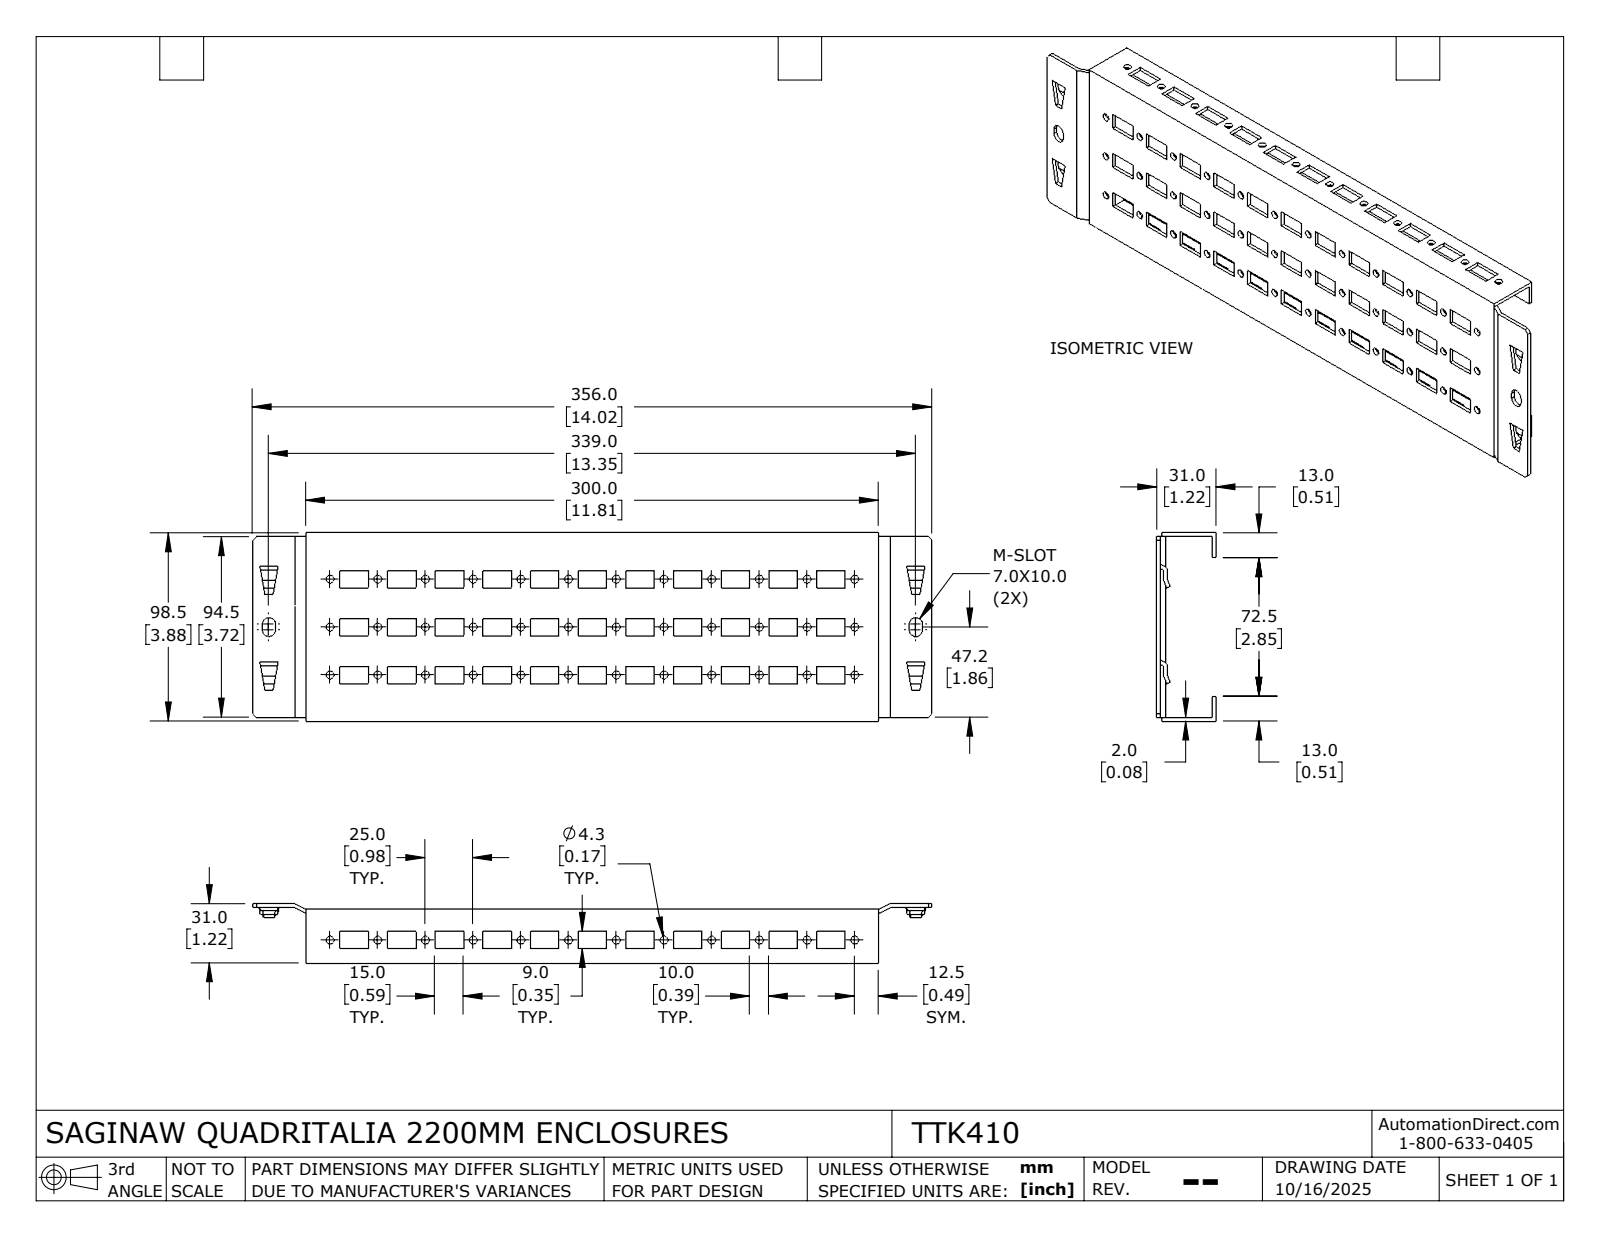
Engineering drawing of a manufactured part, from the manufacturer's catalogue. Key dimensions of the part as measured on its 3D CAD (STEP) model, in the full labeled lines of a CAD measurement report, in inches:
Part name (STEP PRODUCT): TTK410
STEP written by: SolidWorks 2024 (AUTOMOTIVE_DESIGN)
Units: inches
Bodies: 1 solid, 406 faces (338 planar, 68 cylindrical, 0 other)
Overall size (bounding box): 14.016 × 3.878 × 1.22
Volume: 5.954 in³ · Surface area: 166.2 in²
Round holes (diameter × count): ⌀0.167 ×48
Partial cylindrical surfaces — rounded edges, fillets, slot ends (radius × count): R0.138 ×4, R0.079 ×2
Main face-to-face distances: 0.079, 1.024, 3.799, 1.102, 0.118, 1.142, 3.878, 0.945, 3.72, 0.197
Hole centre spacings: 0.984, 2.201, 1.969, 1.392, 2.953, 3.113, 3.937, 4.921
